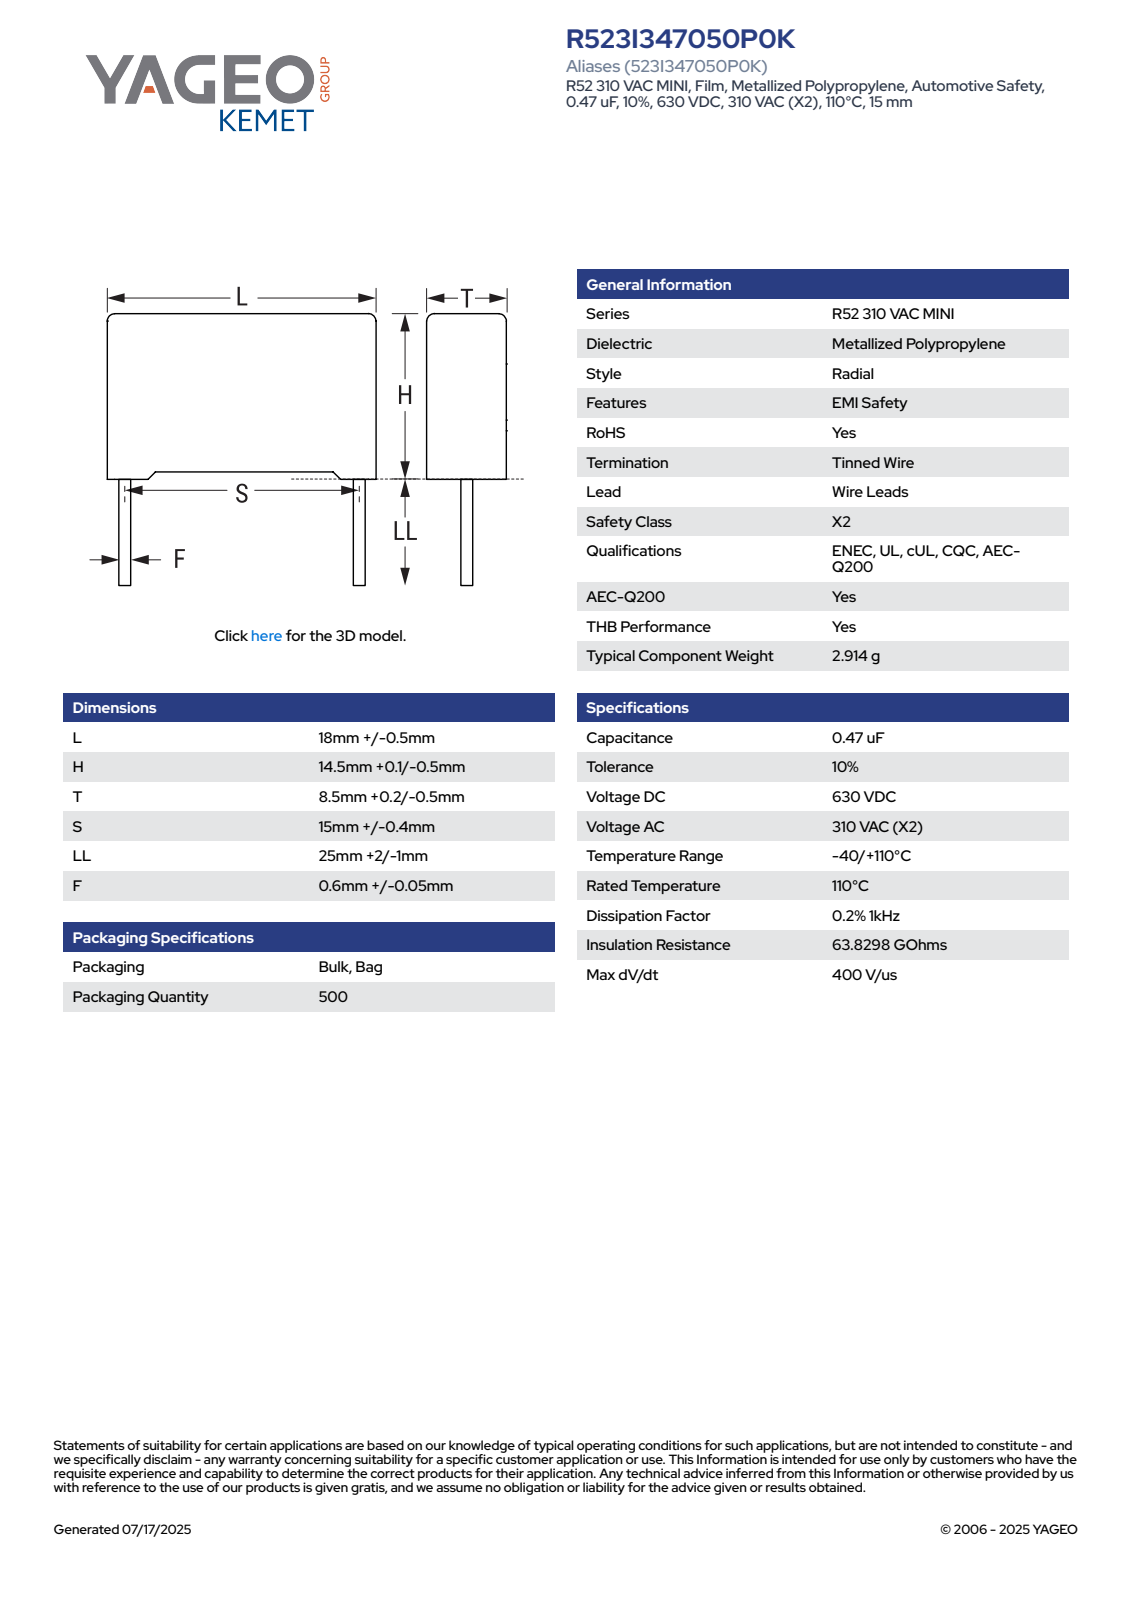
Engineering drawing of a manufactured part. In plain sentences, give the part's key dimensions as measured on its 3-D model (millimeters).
The part is named "CFR_RB2_18X14.5X8.5_L18.5H14.6T8.7S15LL27F0.65". Its 3-D file was written by "SolidWorks 2021 (AUTOMOTIVE_DESIGN)". It is 4 solids with 85 faces: 77 planar, 8 cylindrical and 0 other. Overall it measures 41.6 by 18.5 by 8.71 millimeters. Its volume is 2 262 cubic millimeters and its surface area 1 258 square millimeters. Round bosses or shafts: 2 of diameter 0.65. Partial cylindrical surfaces (rounded edges, fillets, slot ends): 4 of radius 0.5. The main face-to-face distances are 8.7, 13.85, 18.5, 0.62, 0.75, 14.6, 8.08, 0.5, 14.1, 17.88.
